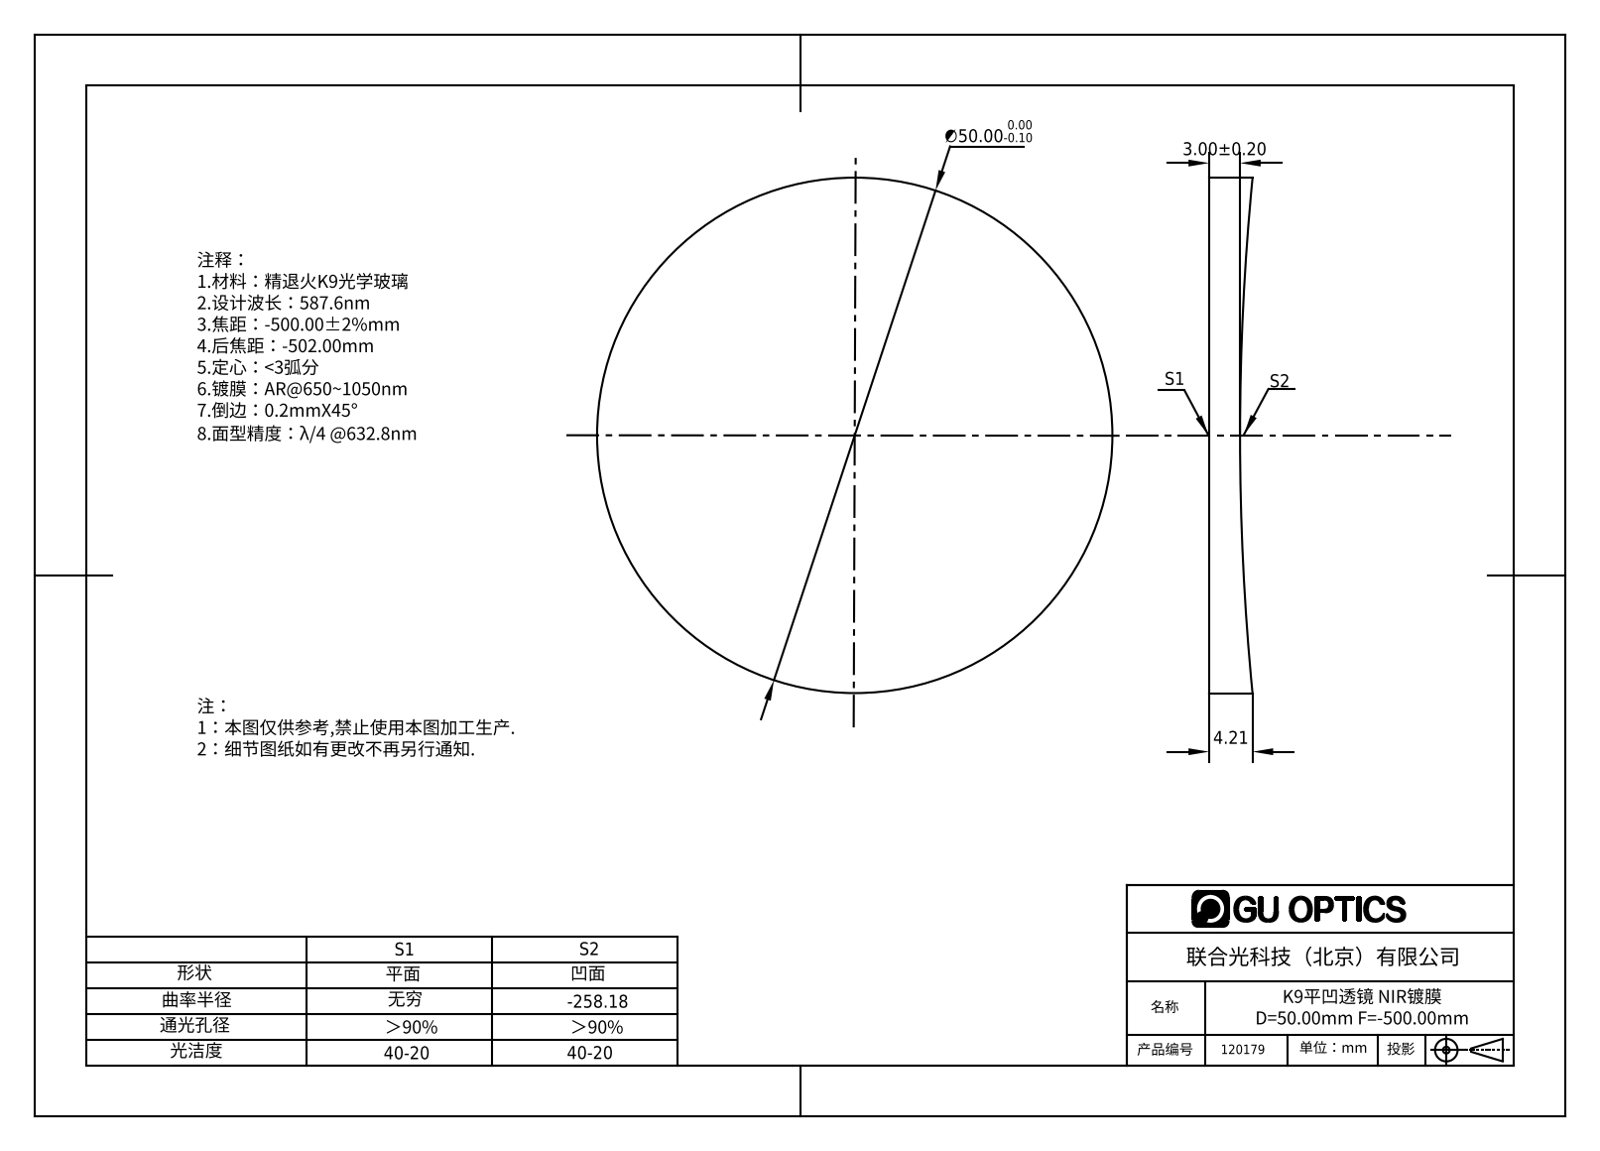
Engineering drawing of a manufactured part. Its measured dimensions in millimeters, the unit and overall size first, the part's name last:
Units: millimetres
Overall size (bounding box): 50 × 50 × 4.21
Round bosses / shafts (diameter × count): ⌀50 ×1
Volume: 7 081 mm³ · Surface area: 4 593 mm²
Bodies: 1 solid, 5 faces (1 planar, 2 cylindrical, 2 other)
Part name (STEP PRODUCT): 120059
STEP written by: SolidWorks 2016 (AUTOMOTIVE_DESIGN)
